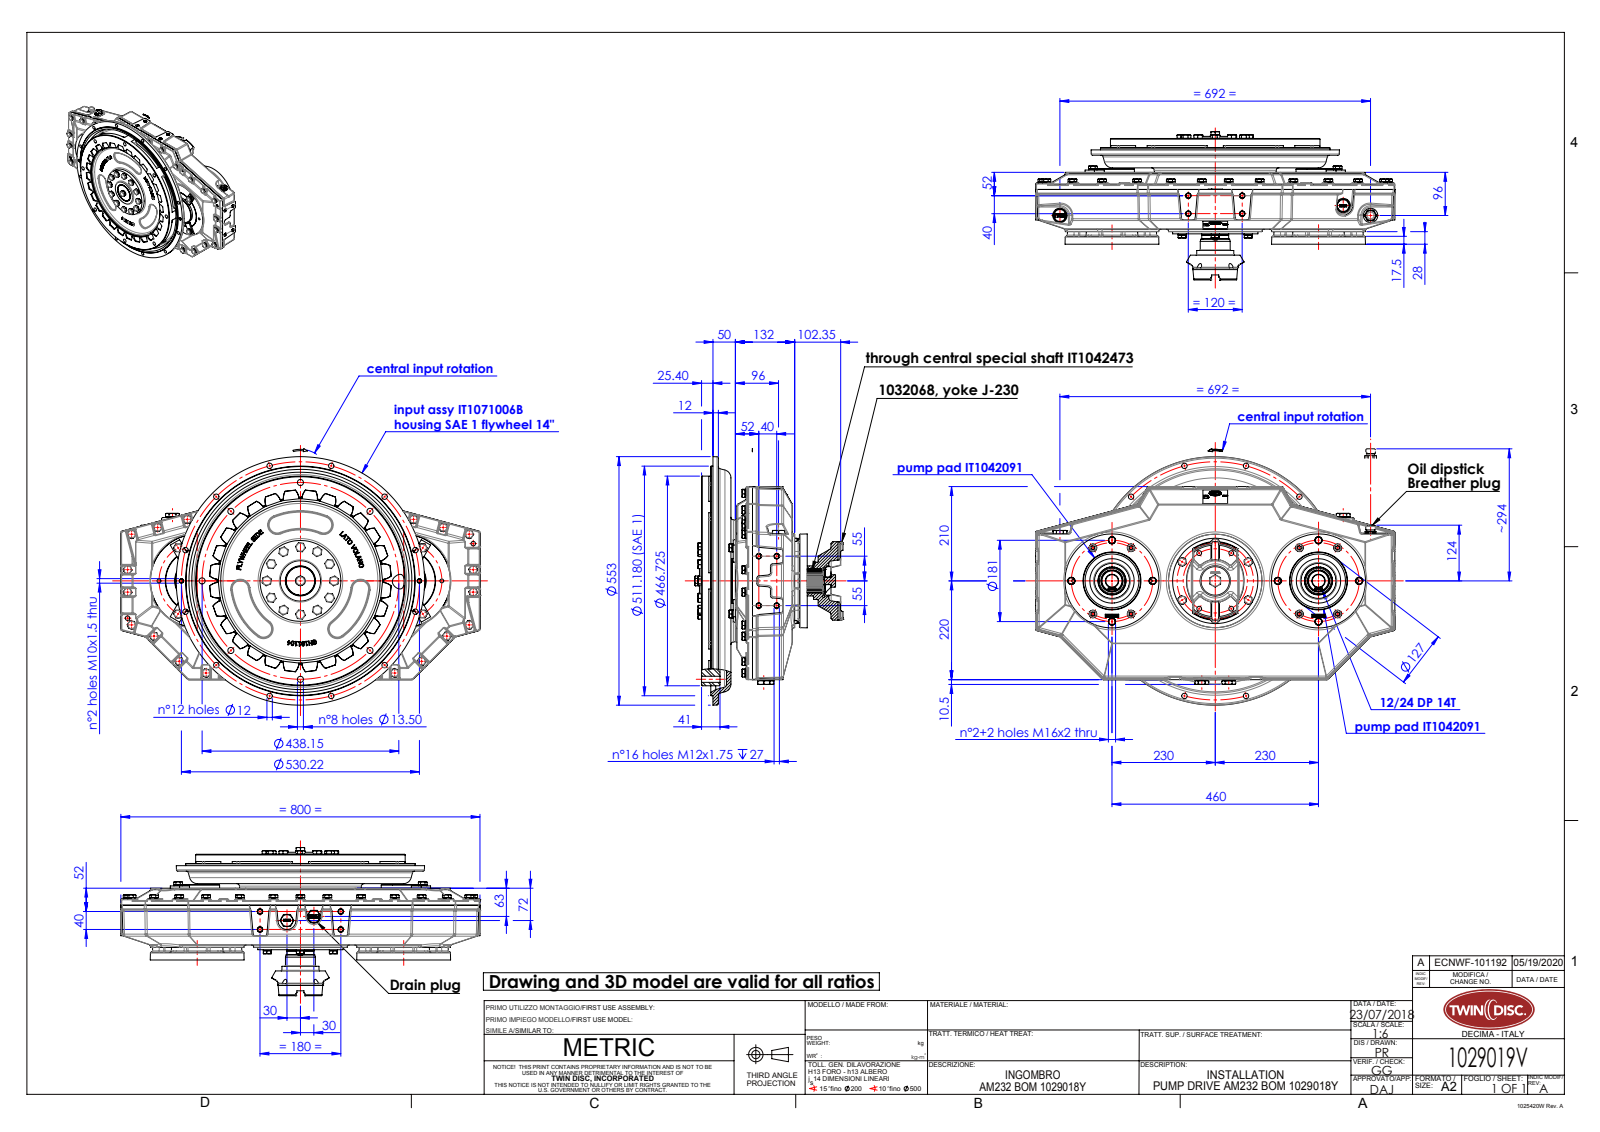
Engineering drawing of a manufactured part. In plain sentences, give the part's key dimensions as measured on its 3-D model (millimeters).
The part is named "ITB00810000_rev01-installation; IT4588040_rev00-installation; 221712A; IT1071006B_rev03-installation (+8 more)". Its 3-D file was written by "SolidWorks 2019 (AUTOMOTIVE_DESIGN)". It is 67 solids with 9580 faces: 3961 planar, 2700 cylindrical and 2919 other. Overall it measures 800 by 571.17 by 330.06 millimeters. Its volume is 10 600 000 cubic millimeters and its surface area 4 029 000 square millimeters. Round holes: 58 of diameter 10.2, 35 of diameter 10.5, 32 of diameter 8.5, 24 of diameter 12, 20 of diameter 13, 10 of diameter 10, 9 of diameter 14, 9 of diameter 17, 8 of diameter 11, 8 of diameter 13.5, 8 of diameter 16, 7 of diameter 12.2. Round bosses or shafts: 45 of diameter 10, 39 of diameter 18.1, 39 of diameter 16.2, 19 of diameter 18, 19 of diameter 12, 12 of diameter 24, 9 of diameter 16, 7 of diameter 21.1. Partial cylindrical surfaces (rounded edges, fillets, slot ends): 284 of radius 2, 112 of radius 0.75, 112 of radius 5, 104 of radius 3, 76 of radius 2.5, 66 of radius 0.25, 66 of radius 12.5, 58 of radius 0.35. The main face-to-face distances are 10, 38, 58, 48, 50.9, 132, 20, 28, 40.9, 142. The hole center spacings are 120, 57.4, 75, 138.58, 40, 150, 207.84, 30.
